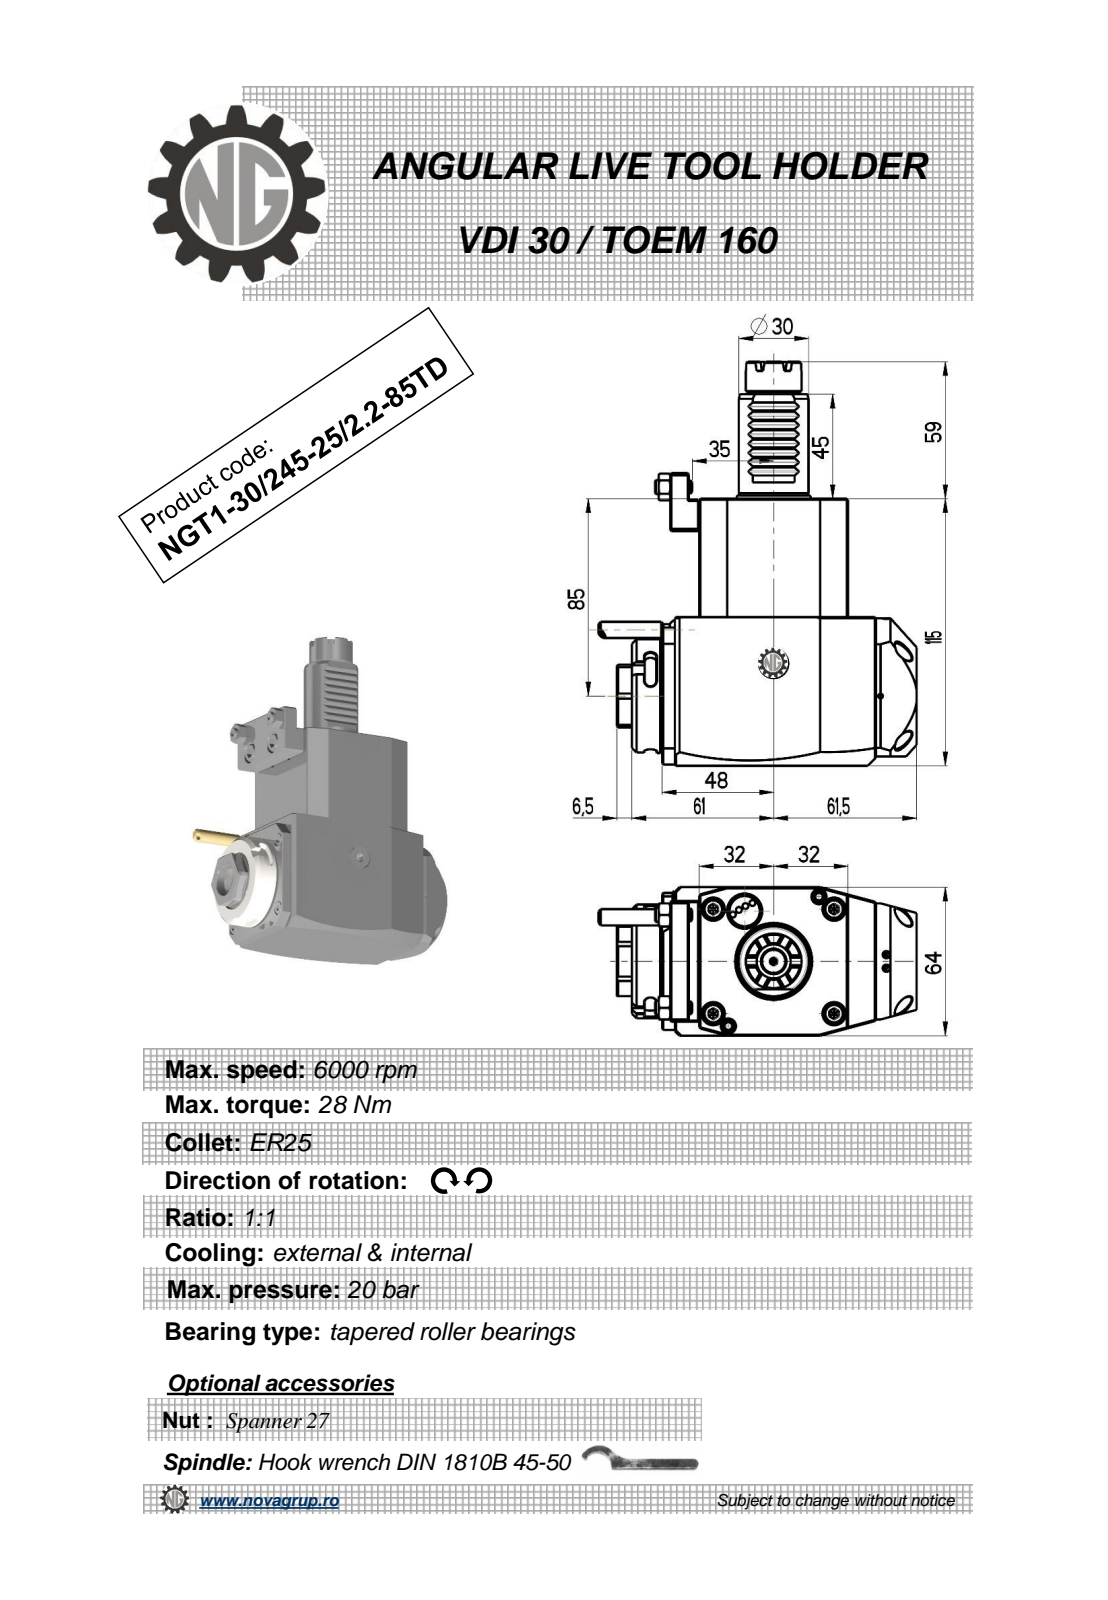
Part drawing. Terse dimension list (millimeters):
name: NGT1_30_245_25_1_2_85TD
written by: PRO/ENGINEER BY PARAMETRIC TECHNOLOGY CORPORATION, 2010280 (CONFIG_CONTROL_DESIGN)
unit: mm
bodies: 1 solid, 384 faces (208 planar, 72 cylindrical, 104 other)
size: 174 × 136.88 × 64
volume: 682 430 mm³; area: 59 069 mm²
holes: 1× ⌀2.5, 1× ⌀3, 1× ⌀18
bosses: 2× ⌀6, 1× ⌀49, 1× ⌀42, 1× ⌀30, 1× ⌀24, 1× ⌀17.7, 1× ⌀15.2, 1× ⌀8
rounds: 10× R0.31, 8× R0.3, 6× R2.5, 2× R180, 1× R4.5, 1× R15, 1× R21.5, 1× R33.5
face distances: 64, 115, 16, 80, 3.5, 13, 16.5, 12.5, 51, 6
hole spacings: 34.25
